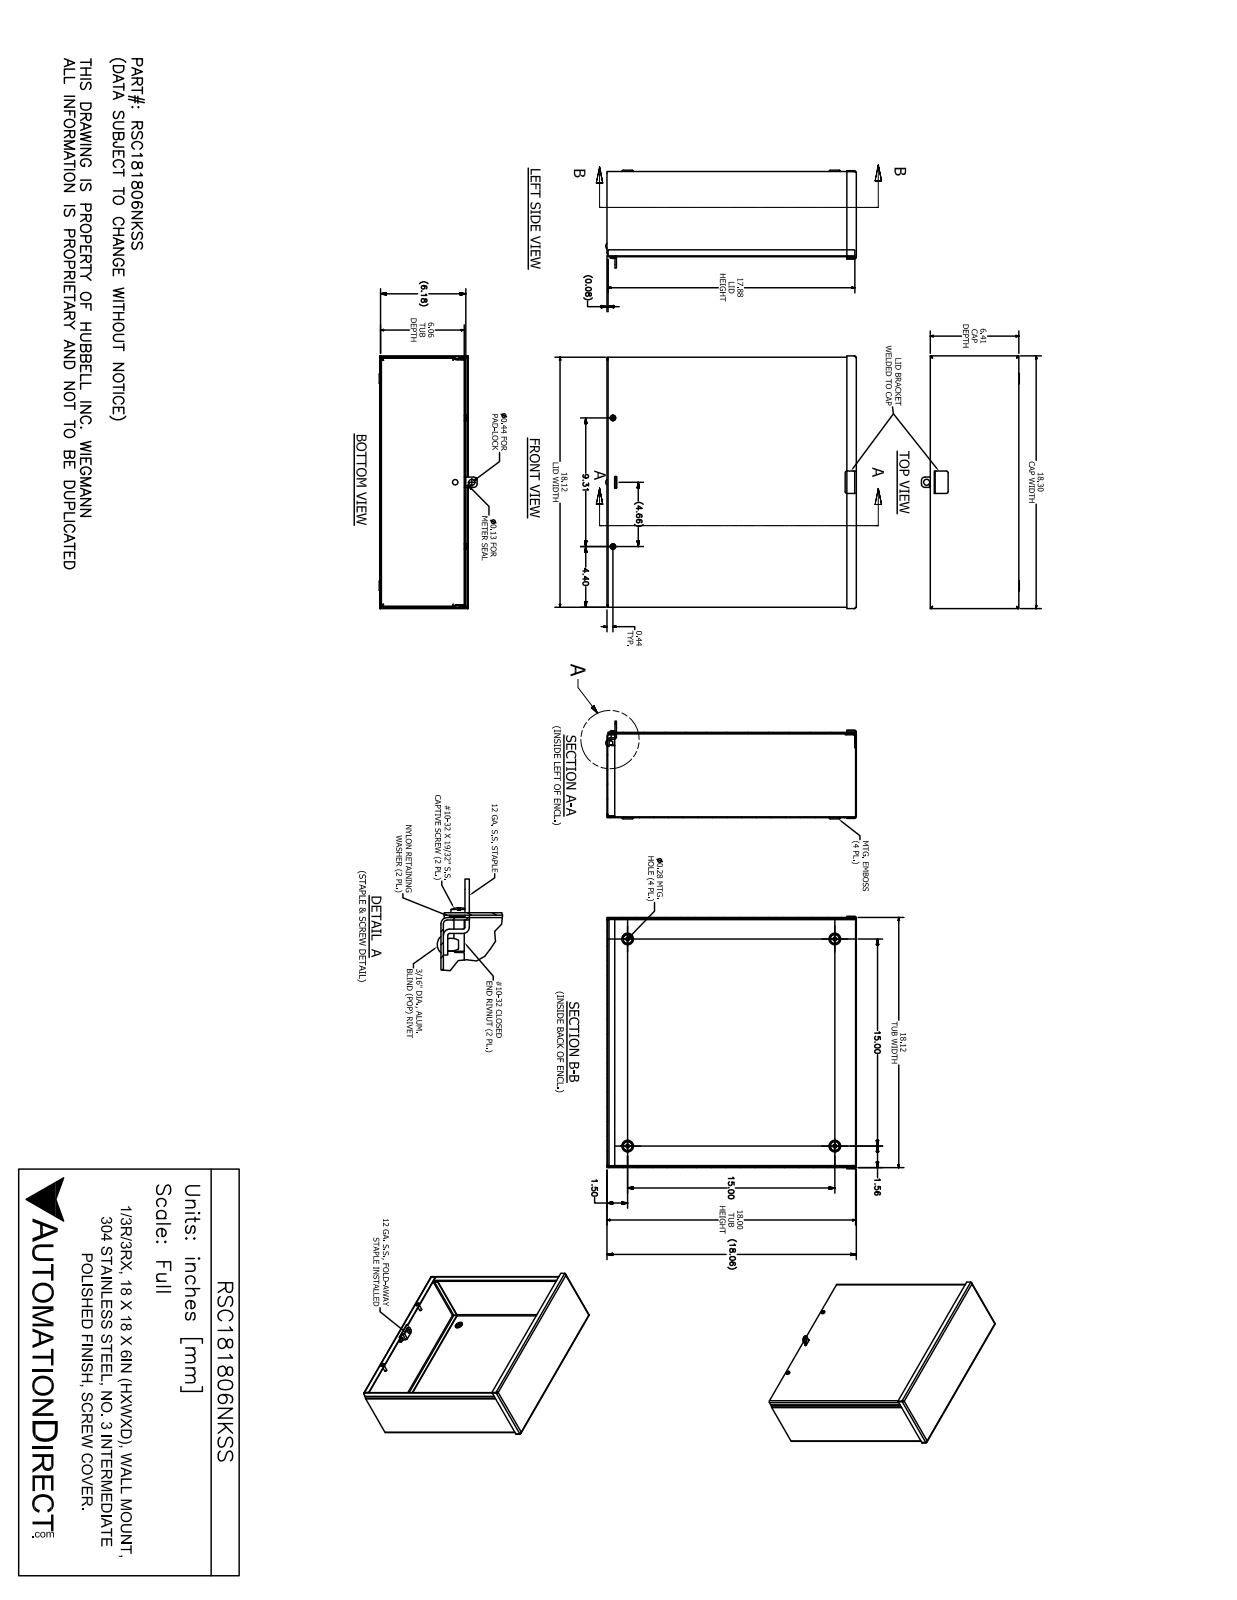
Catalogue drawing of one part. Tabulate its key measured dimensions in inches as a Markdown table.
| quantity | value |
| --- | --- |
| part name | RSC181806NKSS |
| STEP written by | SolidWorks 2017 (AUTOMOTIVE_DESIGN) |
| units | inches |
| bodies | 13 solids, 383 faces (199 planar, 99 cylindrical, 85 other) |
| overall size | 18.299 × 18.149 × 7.084 |
| volume | 68.56 in³ |
| surface area | 2 340 in² |
| round holes (diameter × count) | 0.25 × 4, 0.281 × 4, 0.156 × 2, 0.196 × 2, 0.257 × 2, 0.278 × 2, 0.125 × 1, 0.198 × 1, 0.201 × 1, 0.437 × 1 |
| round bosses / shafts (diameter × count) | 0.453 × 2, 0.406 × 2, 0.248 × 2, 0.167 × 2, 0.187 × 1 |
| partial cylindrical surfaces (radius × count) | 0.094 × 17, 0.153 × 17, 0.031 × 6, 0.125 × 4, 0.25 × 4, 0.047 × 2, 0.05 × 2, 0.062 × 2 |
| main face-to-face distances | 0.059, 6.117, 6.176, 6.058, 18, 18.059, 17.941, 18.118, 0.117, 0.059 |
| hole center spacings | 15, 3.036, 3.047, 9.313, 12.203, 12.206, 16.312, 16.343 |
